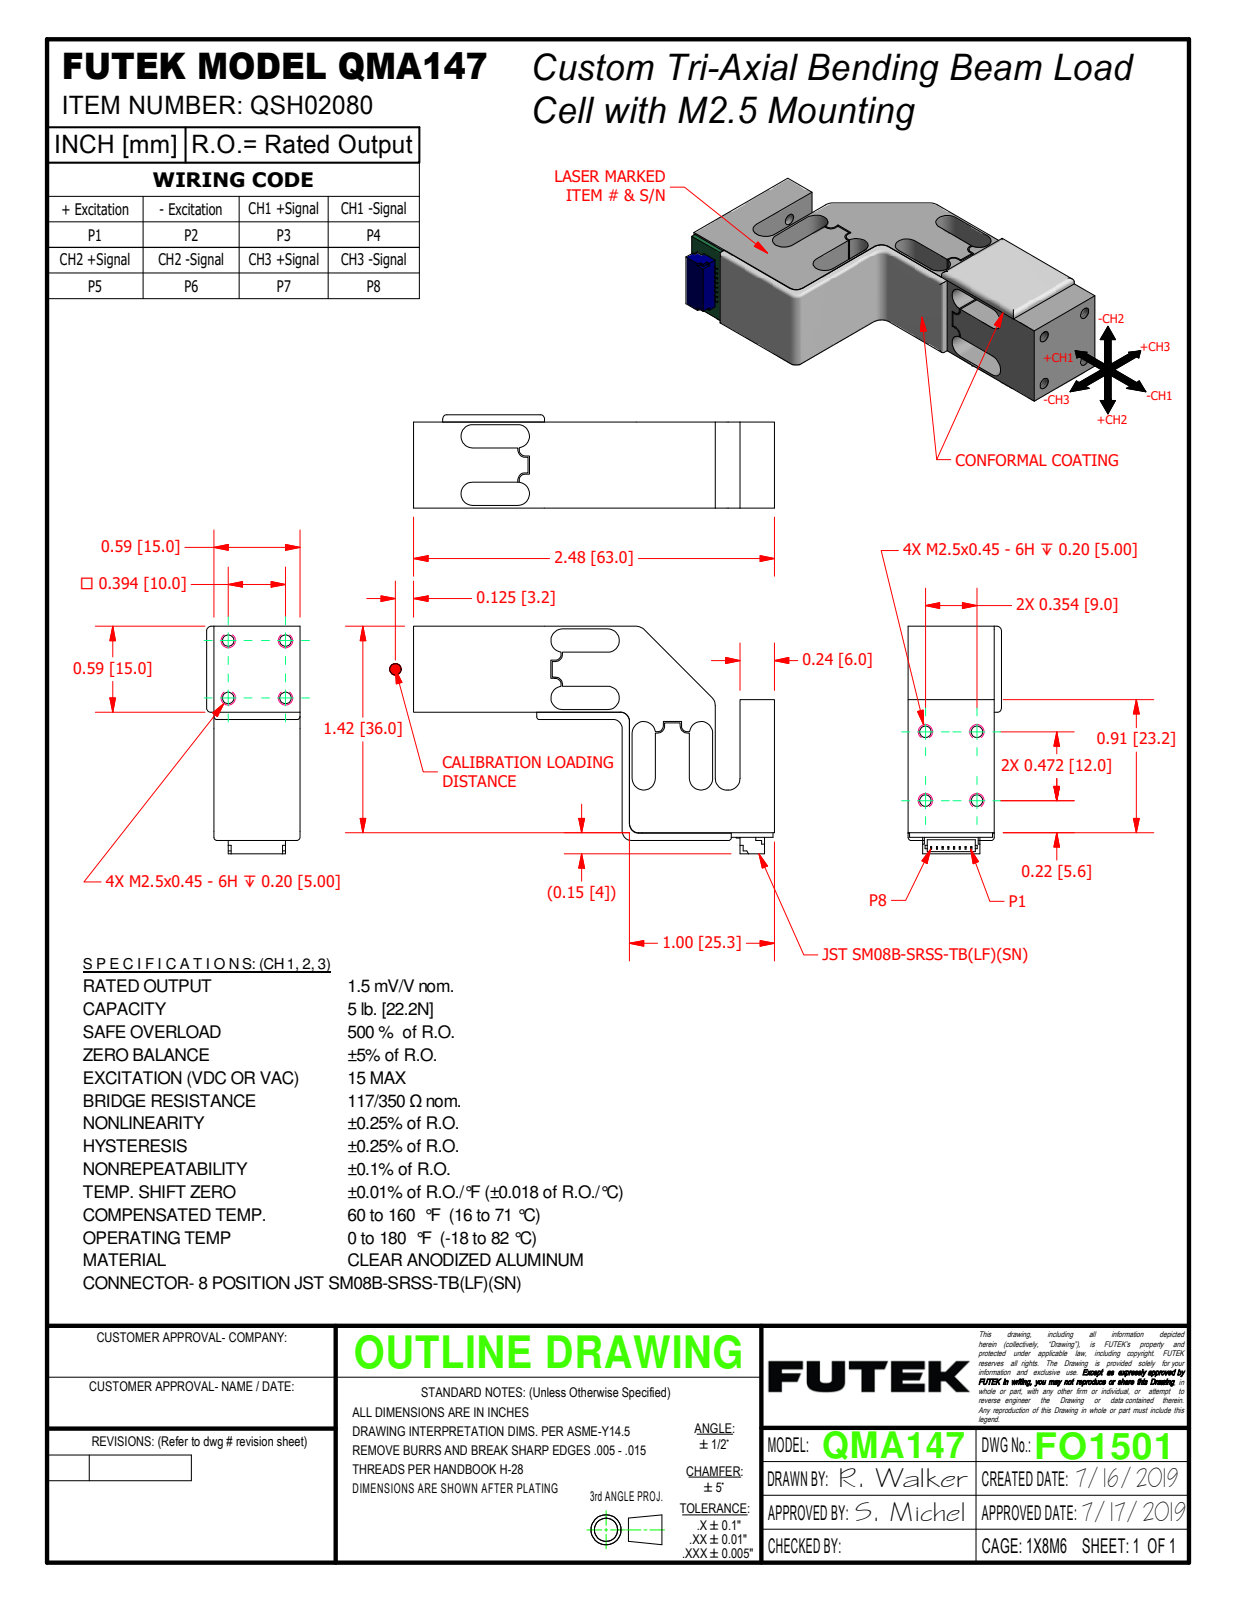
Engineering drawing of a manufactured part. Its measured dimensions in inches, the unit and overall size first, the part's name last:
Units: inches
Overall size (bounding box): 2.48 × 1.563 × 0.641
Round holes (diameter × count): ⌀0.079 ×8
Partial cylindrical surfaces — rounded edges, fillets, slot ends (radius × count): R0.08 ×14, R0.02 ×8, R0.04 ×6, R0.049 ×6, R0.063 ×6, R0.03 ×4
Main face-to-face distances: 0.591, 0.178, 0.05, 0.16, 0.64, 0.412, 0.394, 0.16, 0.228, 0.018
Hole centre spacings: 0.394, 0.233, 0.354, 0.472, 0.557, 0.591, 0.626, 0.705
Volume: 0.921 in³ · Surface area: 14.4 in²
Bodies: 1 solid, 253 faces (185 planar, 58 cylindrical, 10 other)
Part name (STEP PRODUCT): QMA147-Assembly_Shrinkwrap_1
STEP written by: Autodesk Inventor 2018 (AUTOMOTIVE_DESIGN)
